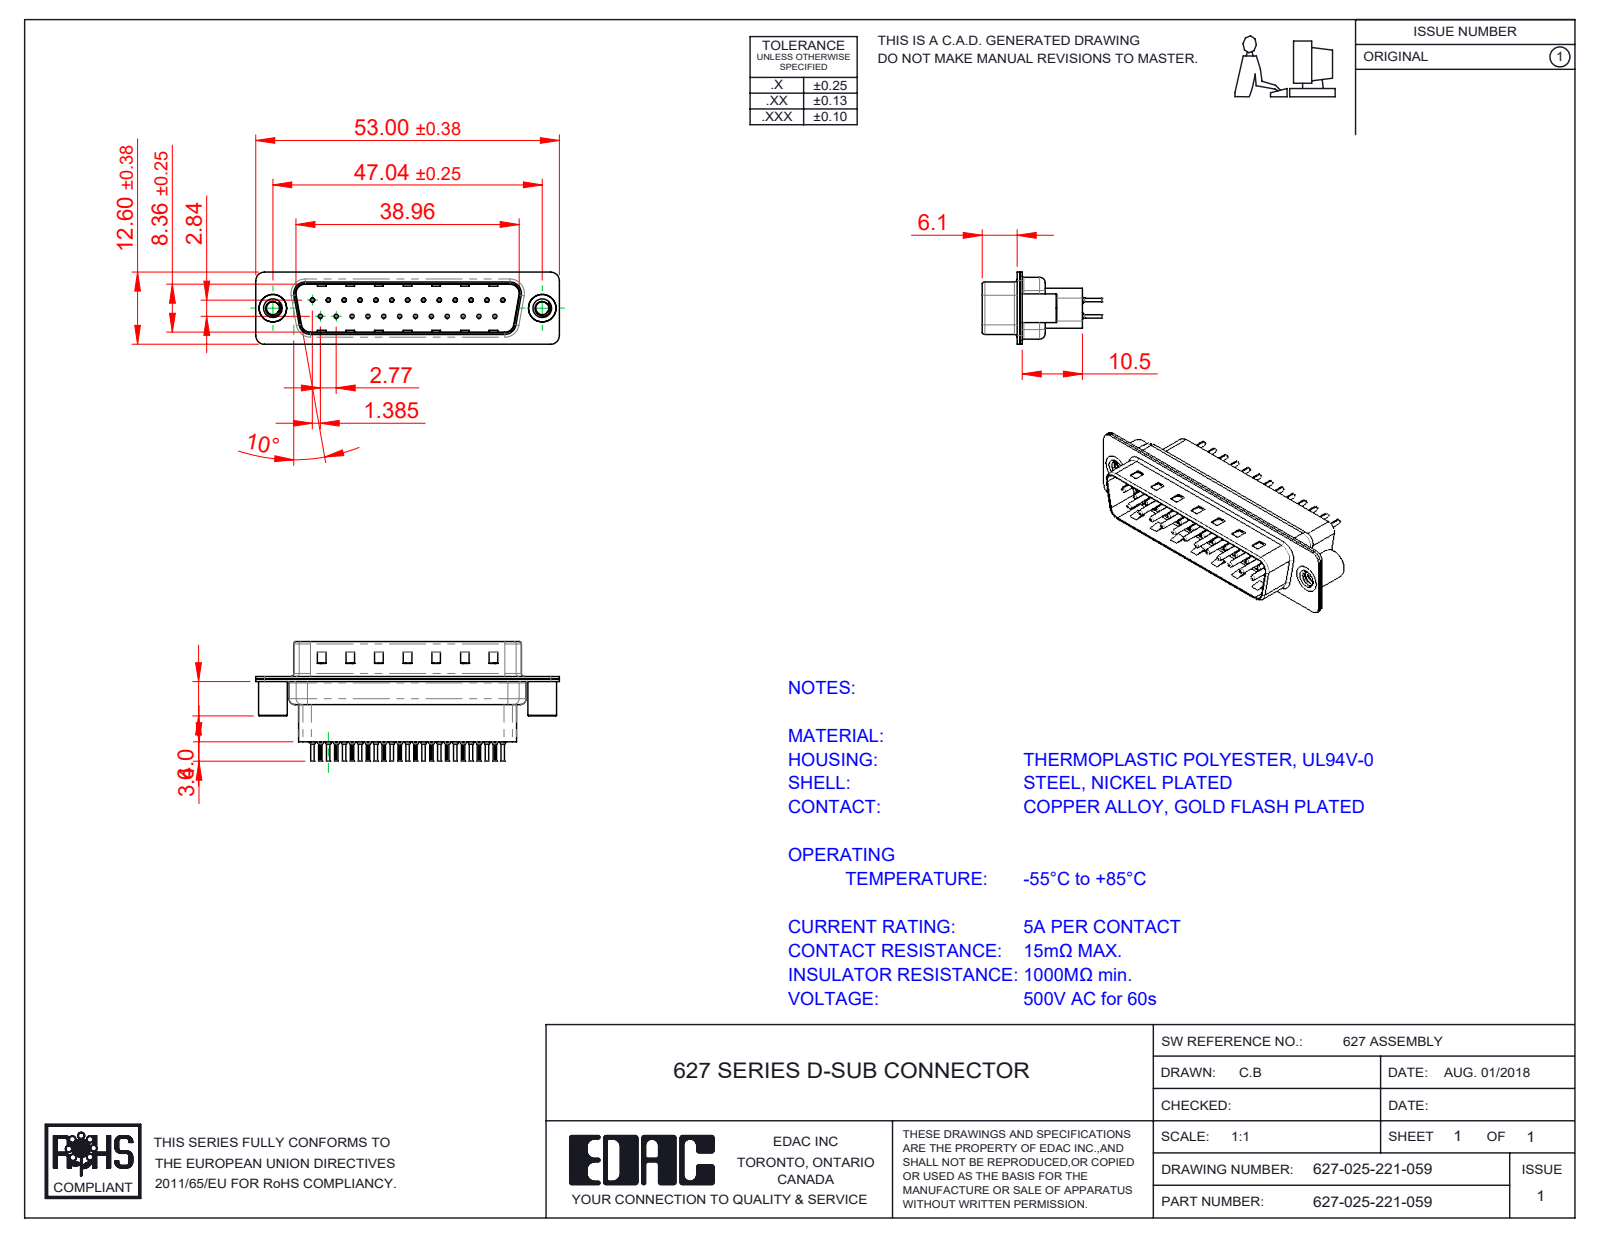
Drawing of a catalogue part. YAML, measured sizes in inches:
part_name: "627 Contact Row 2_21H; 627 4-40 Threaded Standoff BS; 627 Shell Rear_25 Contacts; 627 Housing_25 HP (+3 more)"
step_written_by: "SolidWorks 2020 (CONFIG_CONTROL_DESIGN)"
units: inches
bodies: {solids: 30, faces: 2848, planar: 771, cylindrical: 1082, other: 995}
overall_size: [2.087, 0.819, 0.496]
volume: 0.238
surface_area: 15.45
round_holes:
  - {diameter: 0.008, count: 25}
  - {diameter: 0.014, count: 25}
  - {diameter: 0.043, count: 25}
  - {diameter: 0.063, count: 25}
  - {diameter: 0.089, count: 2}
  - {diameter: 0.157, count: 2}
  - {diameter: 0.189, count: 2}
round_bosses_or_shafts:
  - {diameter: 0.079, count: 25}
  - {diameter: 0.059, count: 25}
  - {diameter: 0.03, count: 25}
  - {diameter: 0.024, count: 25}
  - {diameter: 0.197, count: 2}
  - {diameter: 0.193, count: 2}
partial_cylinders:
  - {radius: 0.004, count: 50}
  - {radius: 0.059, count: 16}
  - {radius: 0.079, count: 12}
  - {radius: 0.02, count: 8}
  - {radius: 0.063, count: 8}
  - {radius: 0.01, count: 4}
  - {radius: 0.024, count: 4}
  - {radius: 0.026, count: 4}
face_to_face_distances: [0.016, 0.018, 0.032, 0.377, 0.027, 0.302, 0.059, 0.035, 0.043, 0.318]
hole_center_spacings: [0.124, 0.327, 0.109, 0.218, 0.436, 0.654, 0.198, 0.198]
